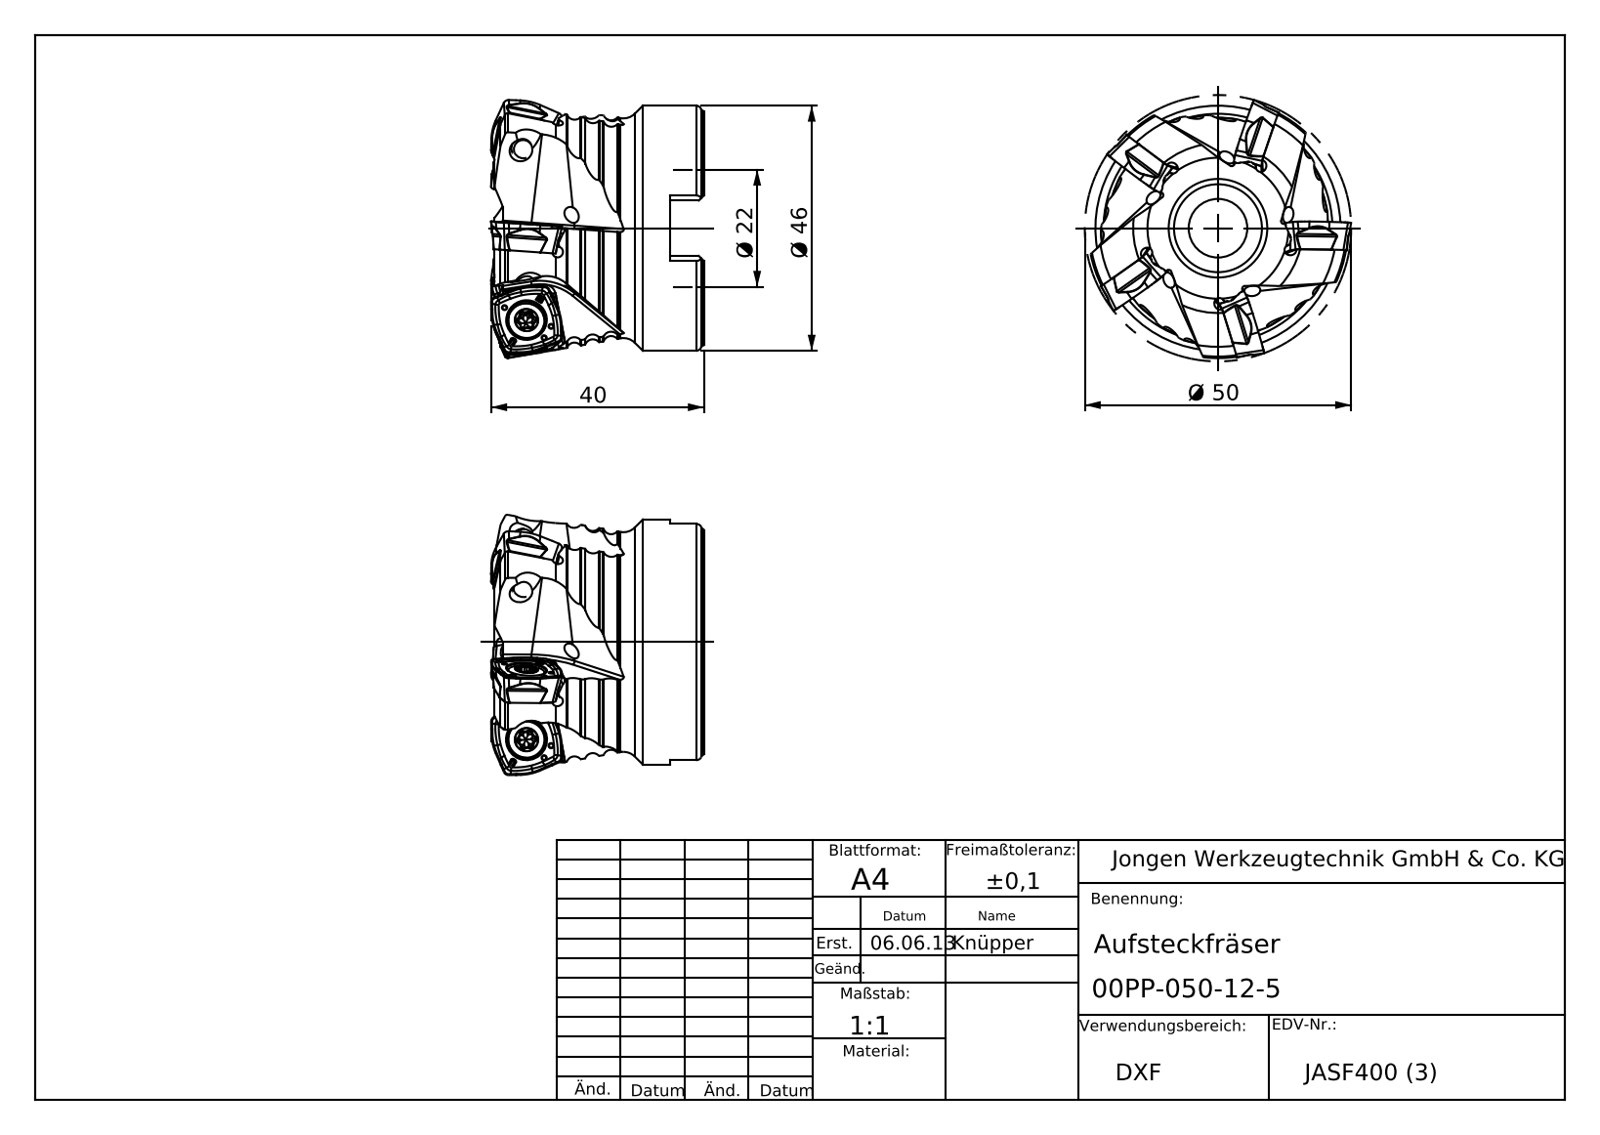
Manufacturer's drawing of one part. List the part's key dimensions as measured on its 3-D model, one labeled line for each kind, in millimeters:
Part name (STEP PRODUCT): 00PP-050-12-5
STEP written by: SolidWorks 2013 (AUTOMOTIVE_DESIGN)
Units: millimetres
Bodies: 1 solid, 284 faces (98 planar, 56 cylindrical, 130 other)
Overall size (bounding box): 49.97 × 49.97 × 39.94
Volume: 47 694 mm³ · Surface area: 12 902 mm²
Round holes (diameter × count): ⌀3 ×5, ⌀11 ×1, ⌀16.5 ×1, ⌀22 ×1, ⌀22.15 ×1, ⌀22.3 ×1
Round bosses / shafts (diameter × count): ⌀46 ×1
Partial cylindrical surfaces — rounded edges, fillets, slot ends (radius × count): R0.5 ×10, R1.3 ×10, R1 ×5, R2 ×5
Main face-to-face distances: 37.75, 6.3, 31.45, 10.4, 27.3, 21, 10.45, 20, 13.7, 7.3
